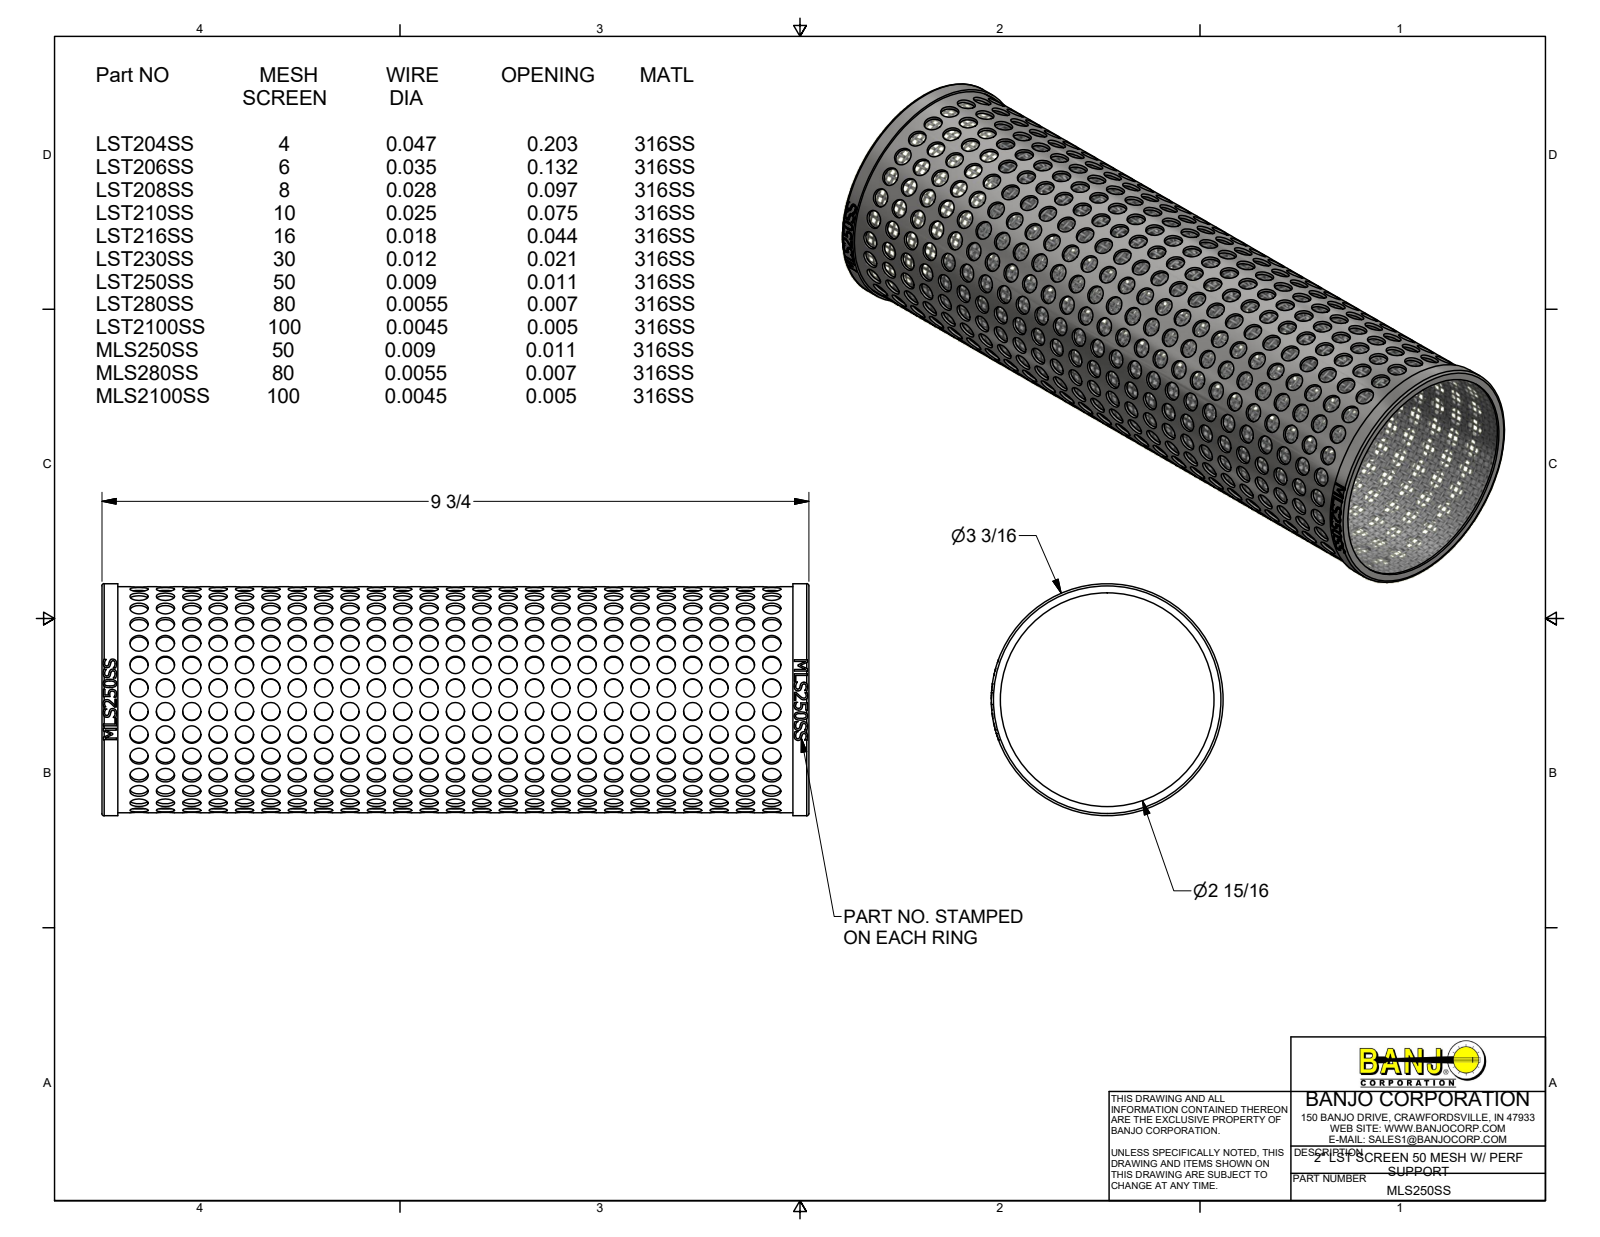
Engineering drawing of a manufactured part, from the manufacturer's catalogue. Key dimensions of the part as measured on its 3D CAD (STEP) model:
Part name (STEP PRODUCT): MLS250SS
STEP written by: Autodesk Inventor 2017 (AUTOMOTIVE_DESIGN)
Units: millimetres
Bodies: 4 solids, 1048 faces (98 planar, 780 cylindrical, 170 other)
Overall size (bounding box): 246.89 × 80.97 × 80.97
Volume: 54 540 mm³ · Surface area: 214 060 mm²
Round holes (diameter × count): ⌀6.35 ×625, ⌀74.61 ×1, ⌀75.9 ×1, ⌀76.91 ×1, ⌀79.45 ×1
Round bosses / shafts (diameter × count): ⌀80.98 ×1, ⌀78.94 ×1, ⌀76.4 ×1
Partial cylindrical surfaces — rounded edges, fillets, slot ends (radius × count): R39.98 ×1
Main face-to-face distances: 0.76, 246.13, 1.02, 245.87, 245.11, 245.37, 246.89, 241.33, 4.54, 5.56
Hole centre spacings: 36.83, 9.21, 27.62, 73.66, 46.04, 110.49, 18.42, 18.41
